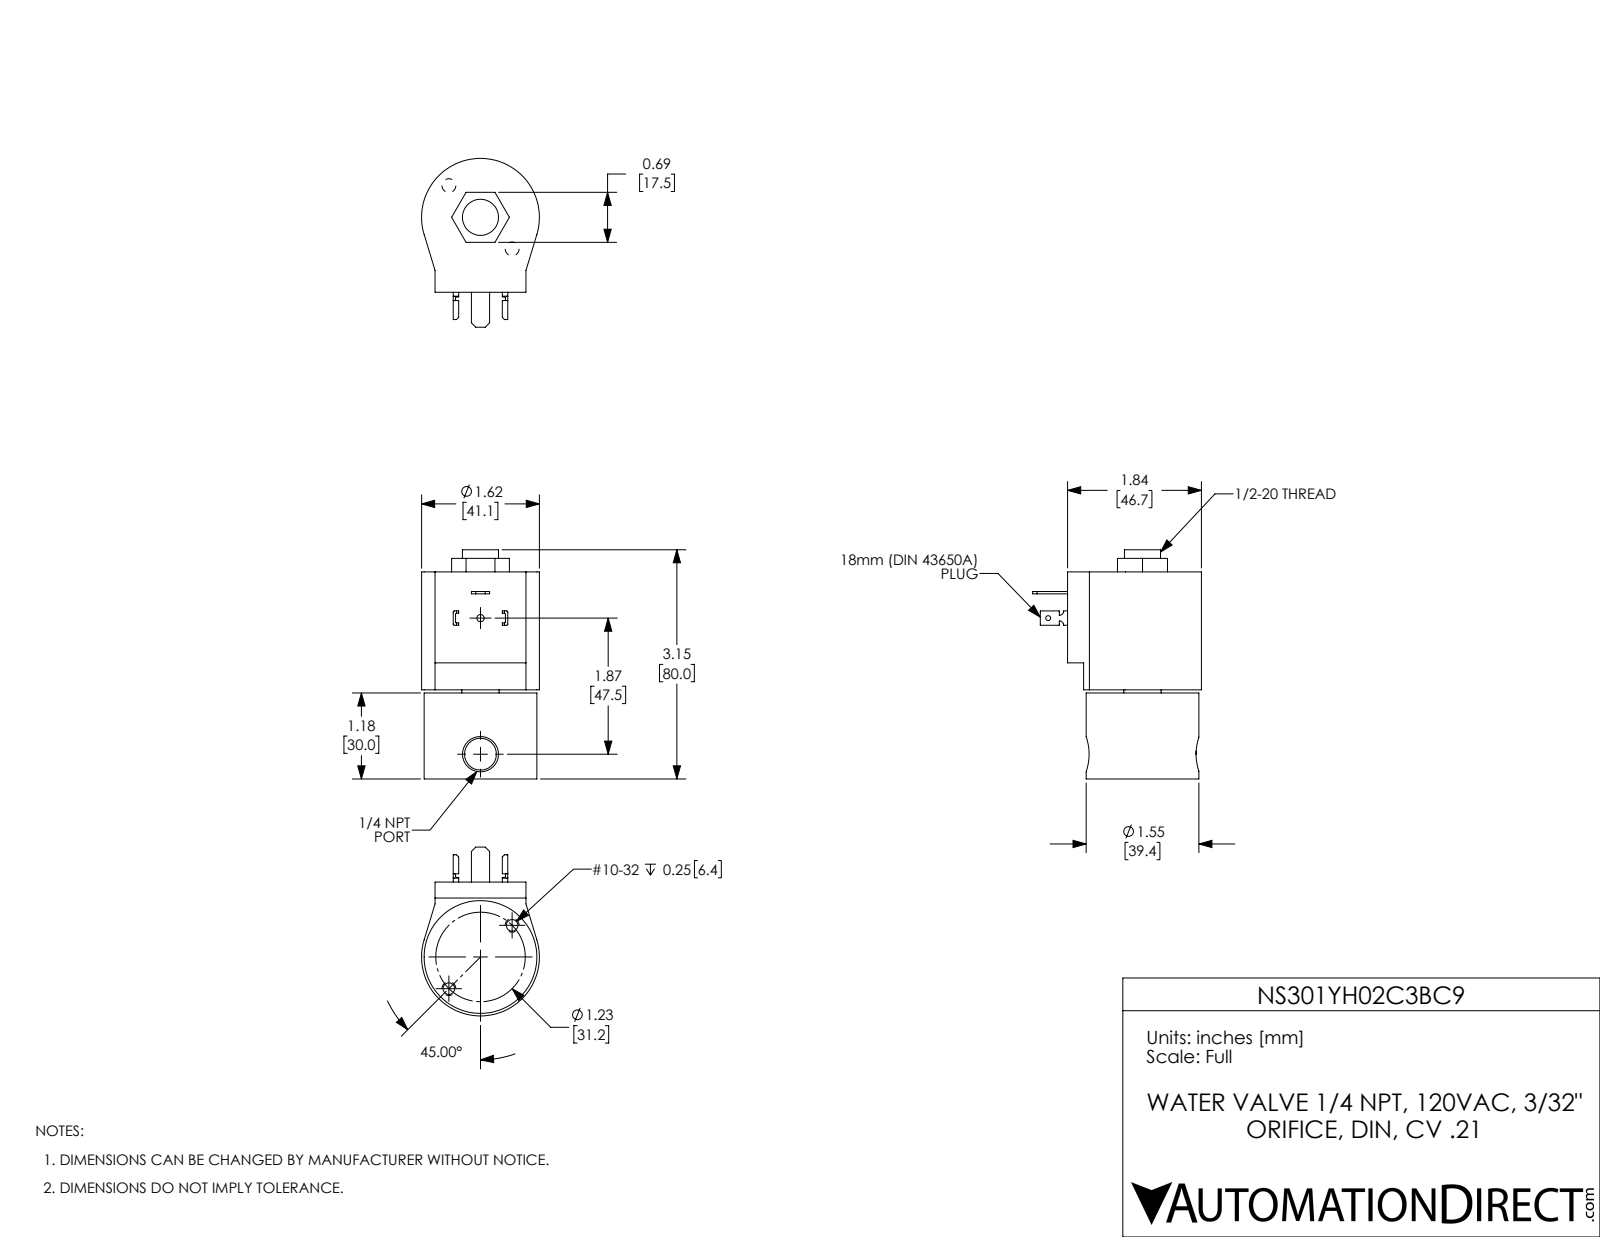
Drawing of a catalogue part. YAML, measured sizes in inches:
part_name: "NS301YH02C3BC9"
step_written_by: "SolidWorks 2024 (CONFIG_CONTROL_DESIGN)"
units: inches
bodies: {solids: 6, faces: 130, planar: 73, cylindrical: 49, other: 8}
overall_size: [3.15, 2.32, 1.62]
volume: 6.027
surface_area: 33.08
round_holes:
  - {diameter: 0.159, count: 2}
  - {diameter: 0.067, count: 1}
  - {diameter: 0.1, count: 1}
  - {diameter: 0.437, count: 1}
  - {diameter: 0.496, count: 1}
  - {diameter: 0.512, count: 1}
  - {diameter: 1.155, count: 1}
round_bosses_or_shafts:
  - {diameter: 1.55, count: 1}
partial_cylinders:
  - {radius: 0.015, count: 8}
  - {radius: 0.06, count: 2}
  - {radius: 0.81, count: 1}
face_to_face_distances: [2.845, 1.182, 1.663, 1.225, 0.043, 1.62, 1.287, 0.106, 0.062, 1.558]
hole_center_spacings: [0.615, 1.23, 1.87]
